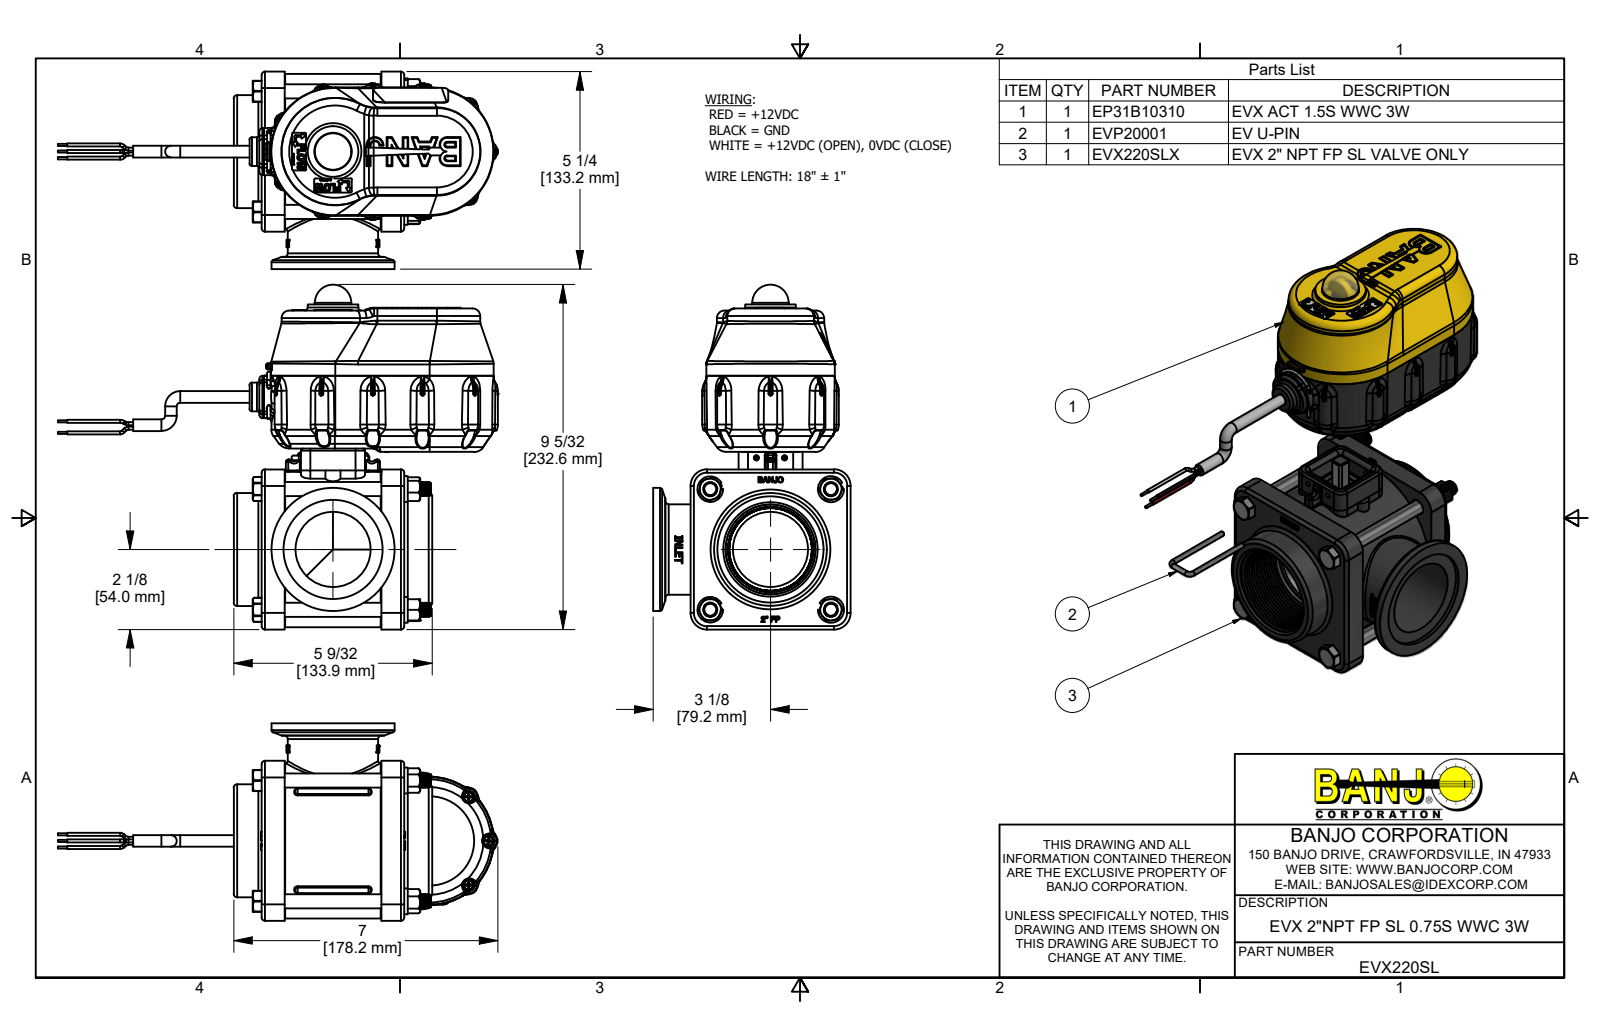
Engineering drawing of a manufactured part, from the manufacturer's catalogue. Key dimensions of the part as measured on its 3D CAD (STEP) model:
Part name (STEP PRODUCT): EVX220SL; EP31B10310; B61905PPHS; B632038PM (+8 more)
STEP written by: Autodesk Inventor 2019 (AUTOMOTIVE_DESIGN)
Units: inches
Bodies: 98 solids, 11984 faces (3422 planar, 3352 cylindrical, 5210 other)
Overall size (bounding box): 11.685 × 9.157 × 5.243
Volume: 76.23 in³ · Surface area: 761 in²
Round holes (diameter × count): ⌀0.095 ×11, ⌀0.15 ×11, ⌀0.08 ×7, ⌀0.107 ×4, ⌀0.126 ×4, ⌀0.136 ×4, ⌀0.148 ×4, ⌀0.15 ×4, ⌀0.17 ×4, ⌀0.307 ×4, ⌀0.385 ×4, ⌀0.438 ×4
Round bosses / shafts (diameter × count): ⌀0.324 ×60, ⌀0.25 ×17, ⌀0.08 ×15, ⌀0.14 ×11, ⌀0.108 ×11, ⌀0.085 ×11, ⌀0.058 ×6, ⌀0.375 ×5
Partial cylindrical surfaces — rounded edges, fillets, slot ends (radius × count): R0.013 ×180, R0.04 ×145, R0.01 ×84, R0.02 ×74, R0.005 ×53, R0.03 ×38, R0.06 ×28, R0.08 ×28
Main face-to-face distances: 0.1, 2.565, 0.61, 3.18, 3.79, 2.485, 0.695, 3.095, 0.085, 0.211
Hole centre spacings: 2.265, 2.69, 2.715, 3.204, 1.662, 1.774, 2.458, 2.73
